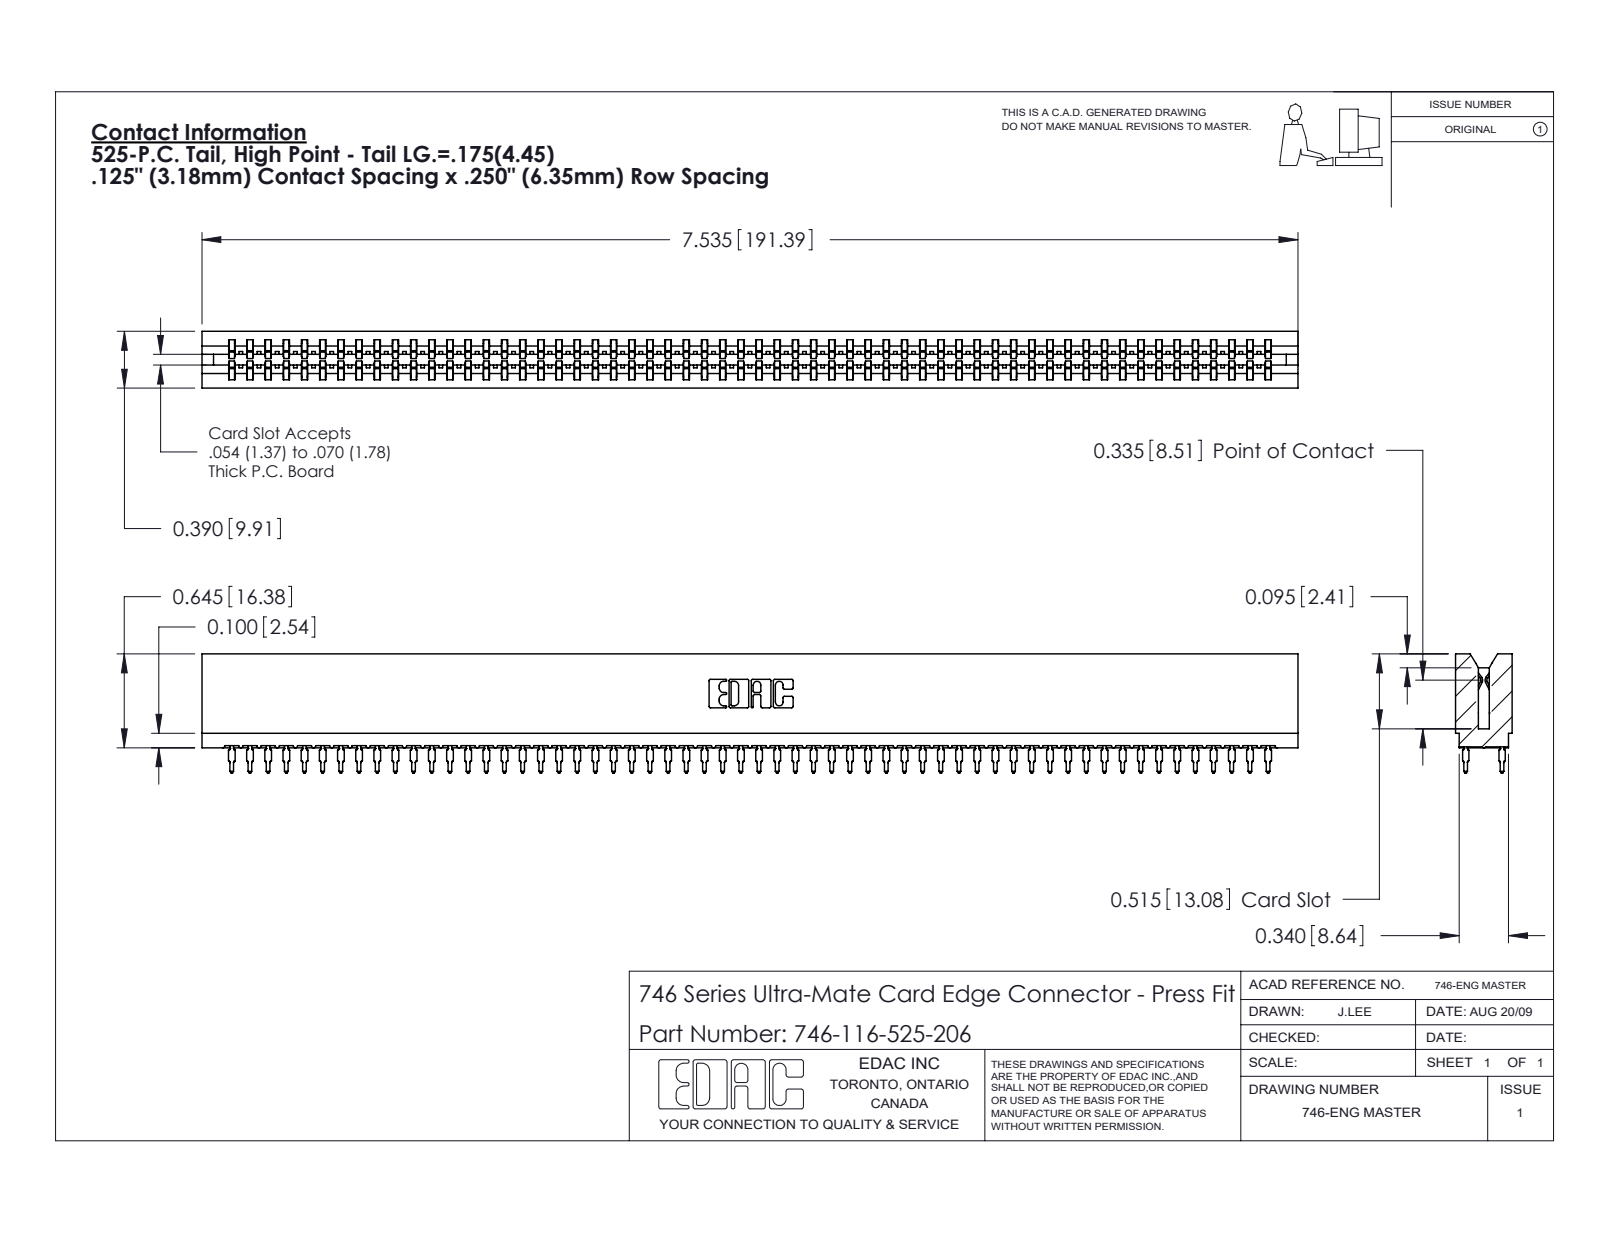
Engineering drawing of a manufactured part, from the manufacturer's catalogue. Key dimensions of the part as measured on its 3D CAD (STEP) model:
Part name (STEP PRODUCT): 746-116-525-206; 746 Part_.515 Slot Depth - 06; 746-292-001_525
STEP written by: SolidWorks 2020 (CONFIG_CONTROL_DESIGN)
Units: inches
Bodies: 117 solids, 10480 faces (5392 planar, 2072 cylindrical, 3016 other)
Overall size (bounding box): 7.535 × 0.819 × 0.39
Volume: 1.24 in³ · Surface area: 50.67 in²
Partial cylindrical surfaces — rounded edges, fillets, slot ends (radius × count): R0.021 ×232, R0.015 ×59, R0.01 ×22, R0.005 ×8, R0.011 ×8, R0.007 ×6, R0.031 ×6, R0.026 ×3
Main face-to-face distances: 0.057, 0.333, 0.39, 0.25, 0.025, 0.307, 0.275, 0.083, 0.174, 0.158
